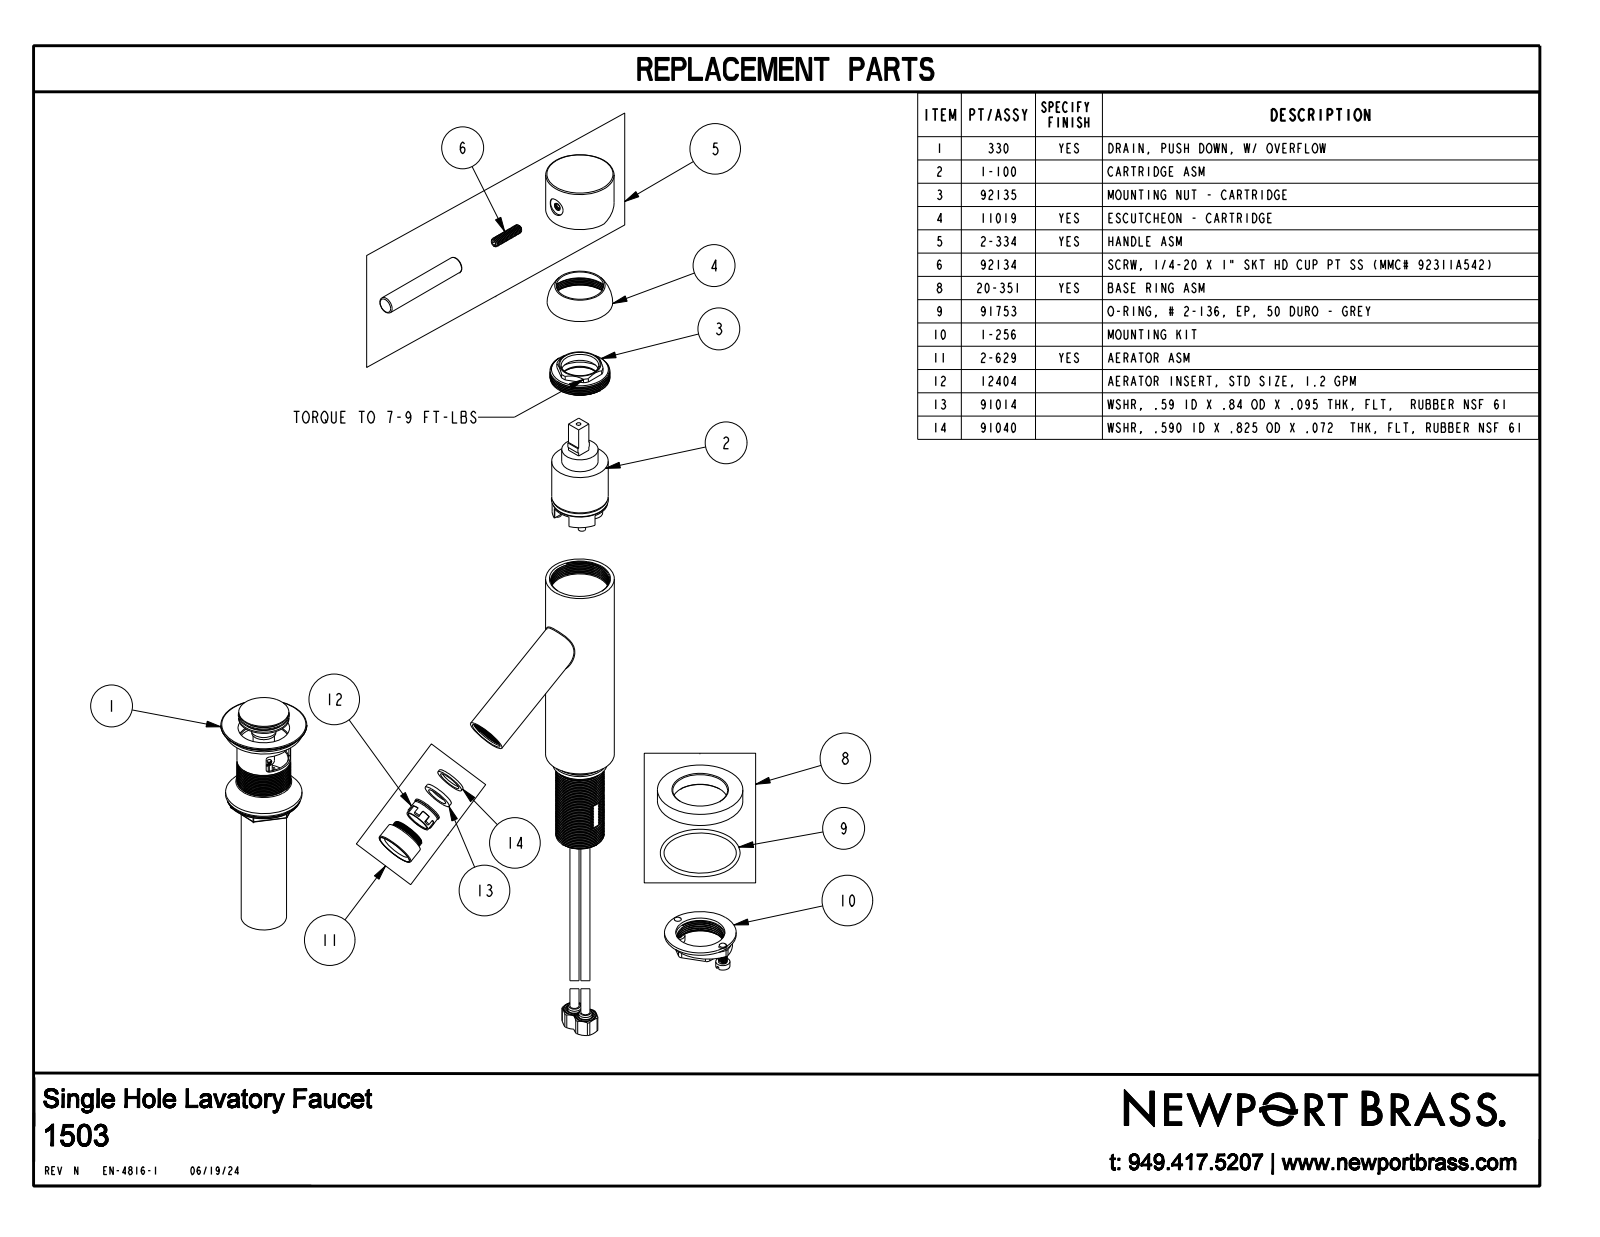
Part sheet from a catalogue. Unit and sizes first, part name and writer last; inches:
Units: inches
Overall size (bounding box): 7.574 × 5.468 × 2.35
Round holes (diameter × count): ⌀0.196 ×1, ⌀1.6 ×1, ⌀1.625 ×1
Round bosses / shafts (diameter × count): ⌀2.35 ×1, ⌀1.89 ×1, ⌀1.88 ×1, ⌀1.1 ×1, ⌀0.7 ×1, ⌀0.465 ×1
Main face-to-face distances: 7.563, 6.275, 1.288, 7.143, 0.868, 0.42, 0.375, 5.9, 6.768, 7.188
Volume: 24.1 in³ · Surface area: 85.59 in²
Bodies: 1 solid, 58 faces (15 planar, 19 cylindrical, 24 other)
Part name (STEP PRODUCT): 1503_SW0001
STEP written by: CREO PARAMETRIC BY PTC INC, 2018400 (AUTOMOTIVE_DESIGN)
